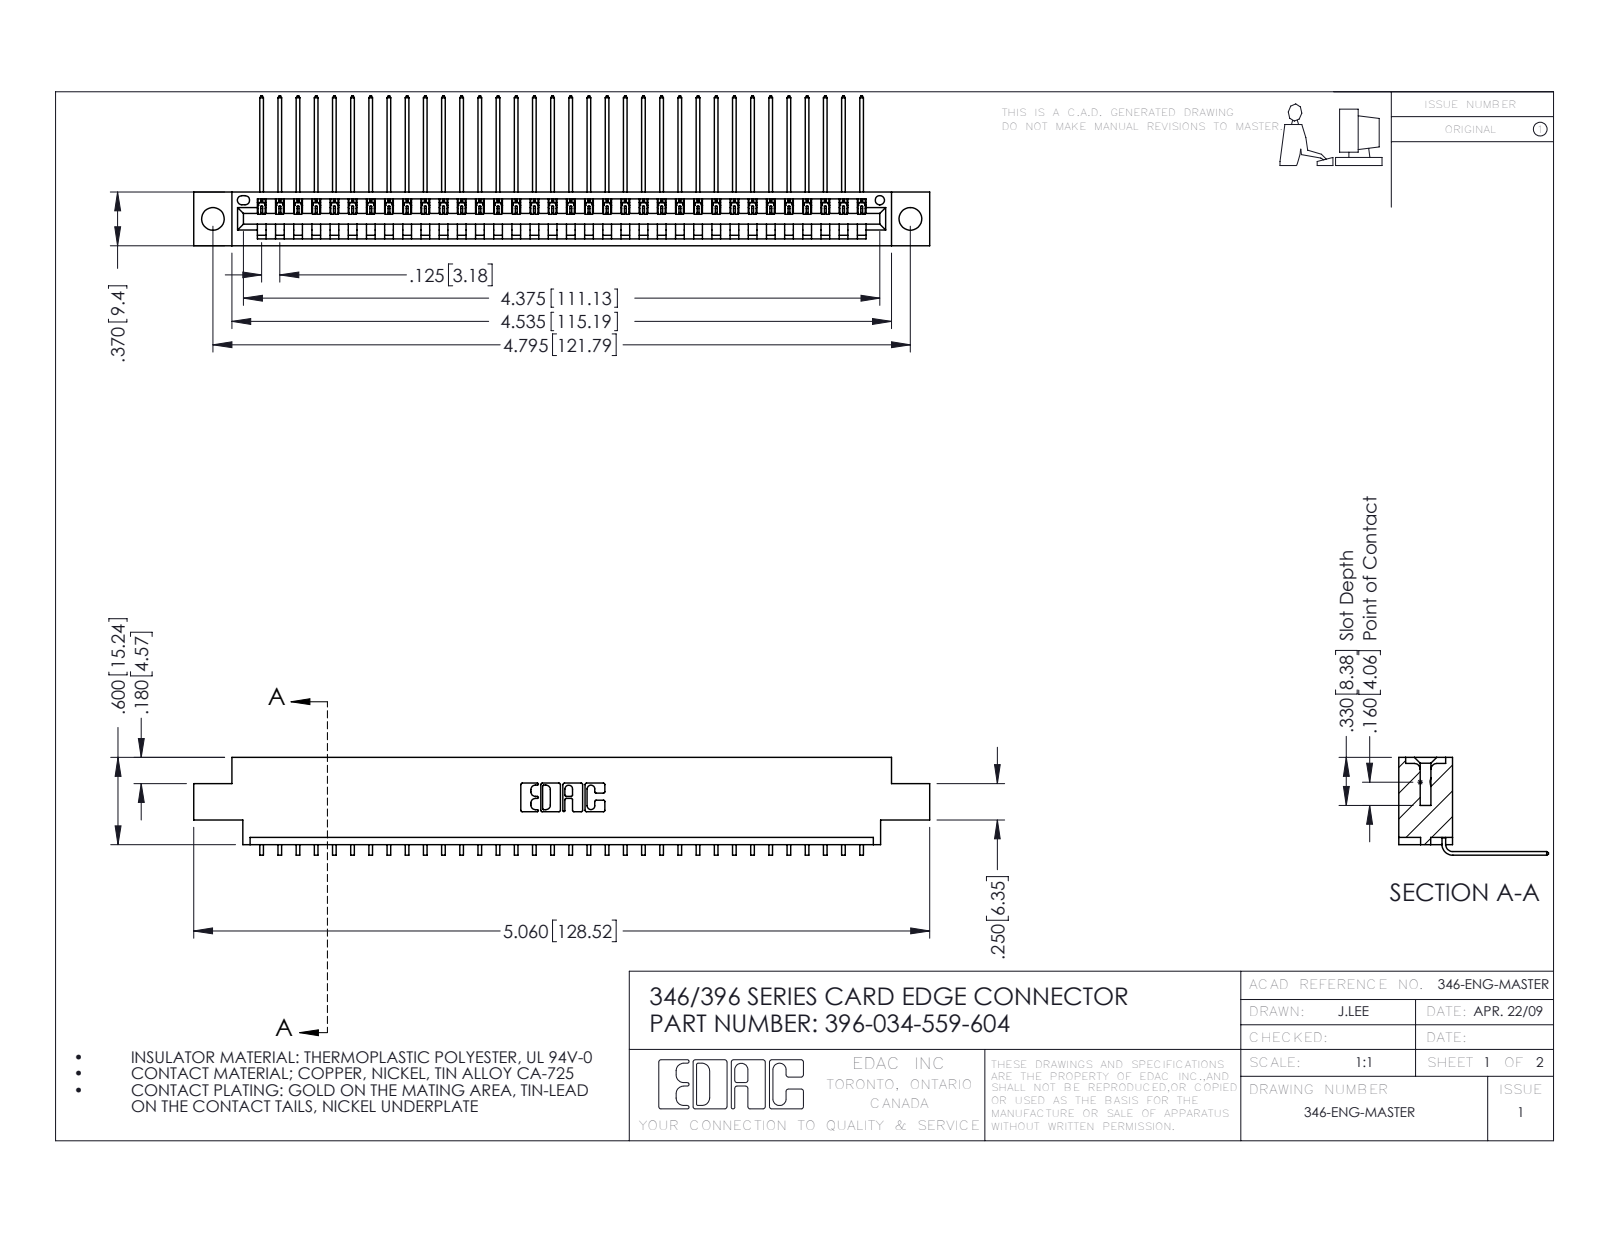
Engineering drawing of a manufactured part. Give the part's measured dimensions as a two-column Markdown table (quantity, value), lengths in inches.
| quantity | value |
| --- | --- |
| part name | 346 Part_0.170 Offset - 0.156 Dia-TH; 396-034-559-604; 345-292-001_558 559 Tail - 1 |
| STEP written by | SolidWorks 2016 (CONFIG_CONTROL_DESIGN) |
| units | inches |
| bodies | 35 solids, 2166 faces (1508 planar, 658 cylindrical, 0 other) |
| overall size | 5.06 × 1.03 × 0.673 |
| volume | 0.74 in³ |
| surface area | 24.34 in² |
| round holes (diameter × count) | 0.156 × 2, 0.064 × 1 |
| partial cylindrical surfaces (radius × count) | 0.006 × 68, 0.01 × 22, 0.007 × 6, 0.031 × 6, 0.026 × 3, 0.031 × 2, 0.04 × 2, 0.014 × 1 |
| main face-to-face distances | 0.048, 0.322, 0.37, 0.25, 0.025, 0.072, 0.298, 0.148, 0.222, 0.1 |
| hole center spacings | 0.246, 4.587, 4.795 |
